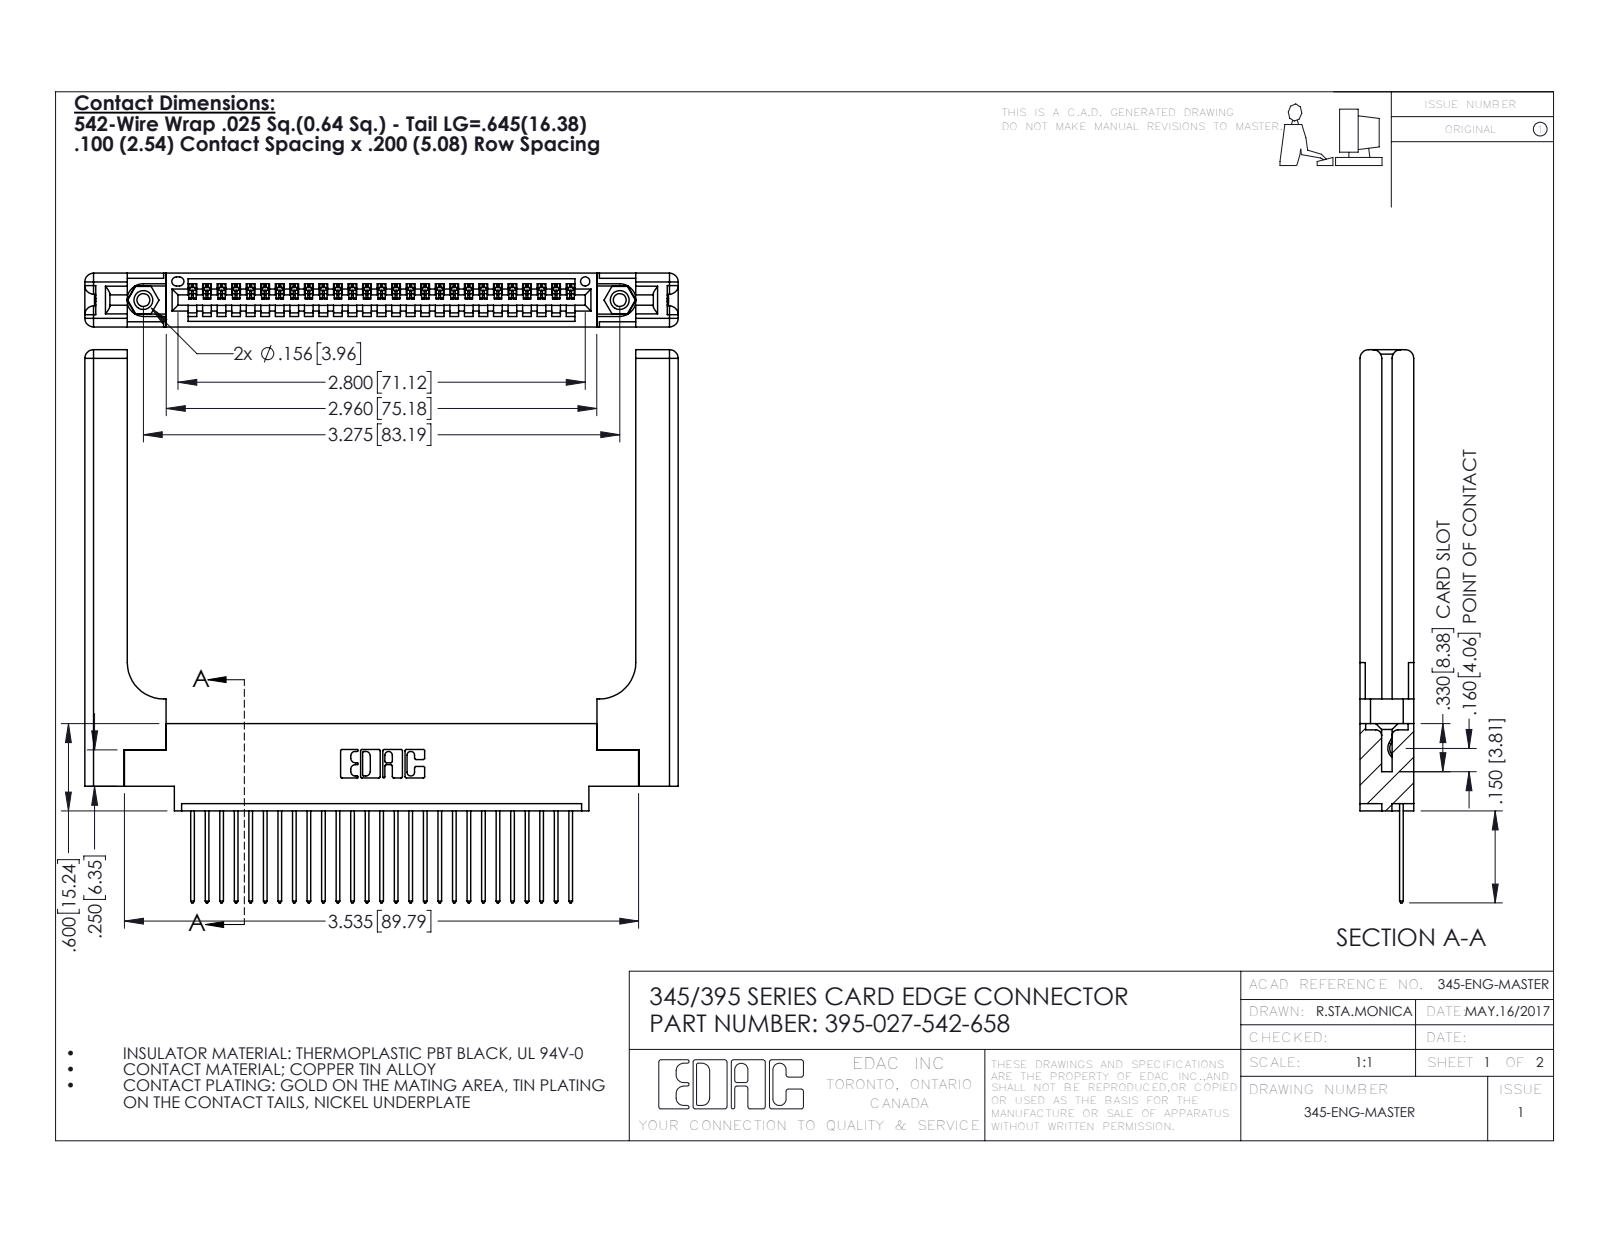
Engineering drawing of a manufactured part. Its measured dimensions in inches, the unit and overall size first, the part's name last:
Units: inches
Overall size (bounding box): 4.079 × 3.802 × 0.37
Round holes (diameter × count): ⌀0.089 ×2, ⌀0.125 ×2, ⌀0.156 ×2, ⌀0.064 ×1
Round bosses / shafts (diameter × count): ⌀0.155 ×2
Partial cylindrical surfaces — rounded edges, fillets, slot ends (radius × count): R0.006 ×54, R0.01 ×54, R0.01 ×22, R0.06 ×16, R0.007 ×6, R0.031 ×6, R0.026 ×3, R0.03 ×2
Main face-to-face distances: 0.37, 0.072, 0.298, 0.098, 0.272, 0.025, 0.2, 0.148, 0.15, 0.077
Hole centre spacings: 0.27, 3.04, 3.275
Volume: 1.109 in³ · Surface area: 28.6 in²
Bodies: 32 solids, 1952 faces (1312 planar, 580 cylindrical, 60 other)
Part name (STEP PRODUCT): 345-292-001_345-293-142; 395-027-542-658; 345-220-058_345-220-058; 345 Part_0.170 Offset - 0.156 Dia-TH (+1 more)
STEP written by: SolidWorks 2016 (CONFIG_CONTROL_DESIGN)
